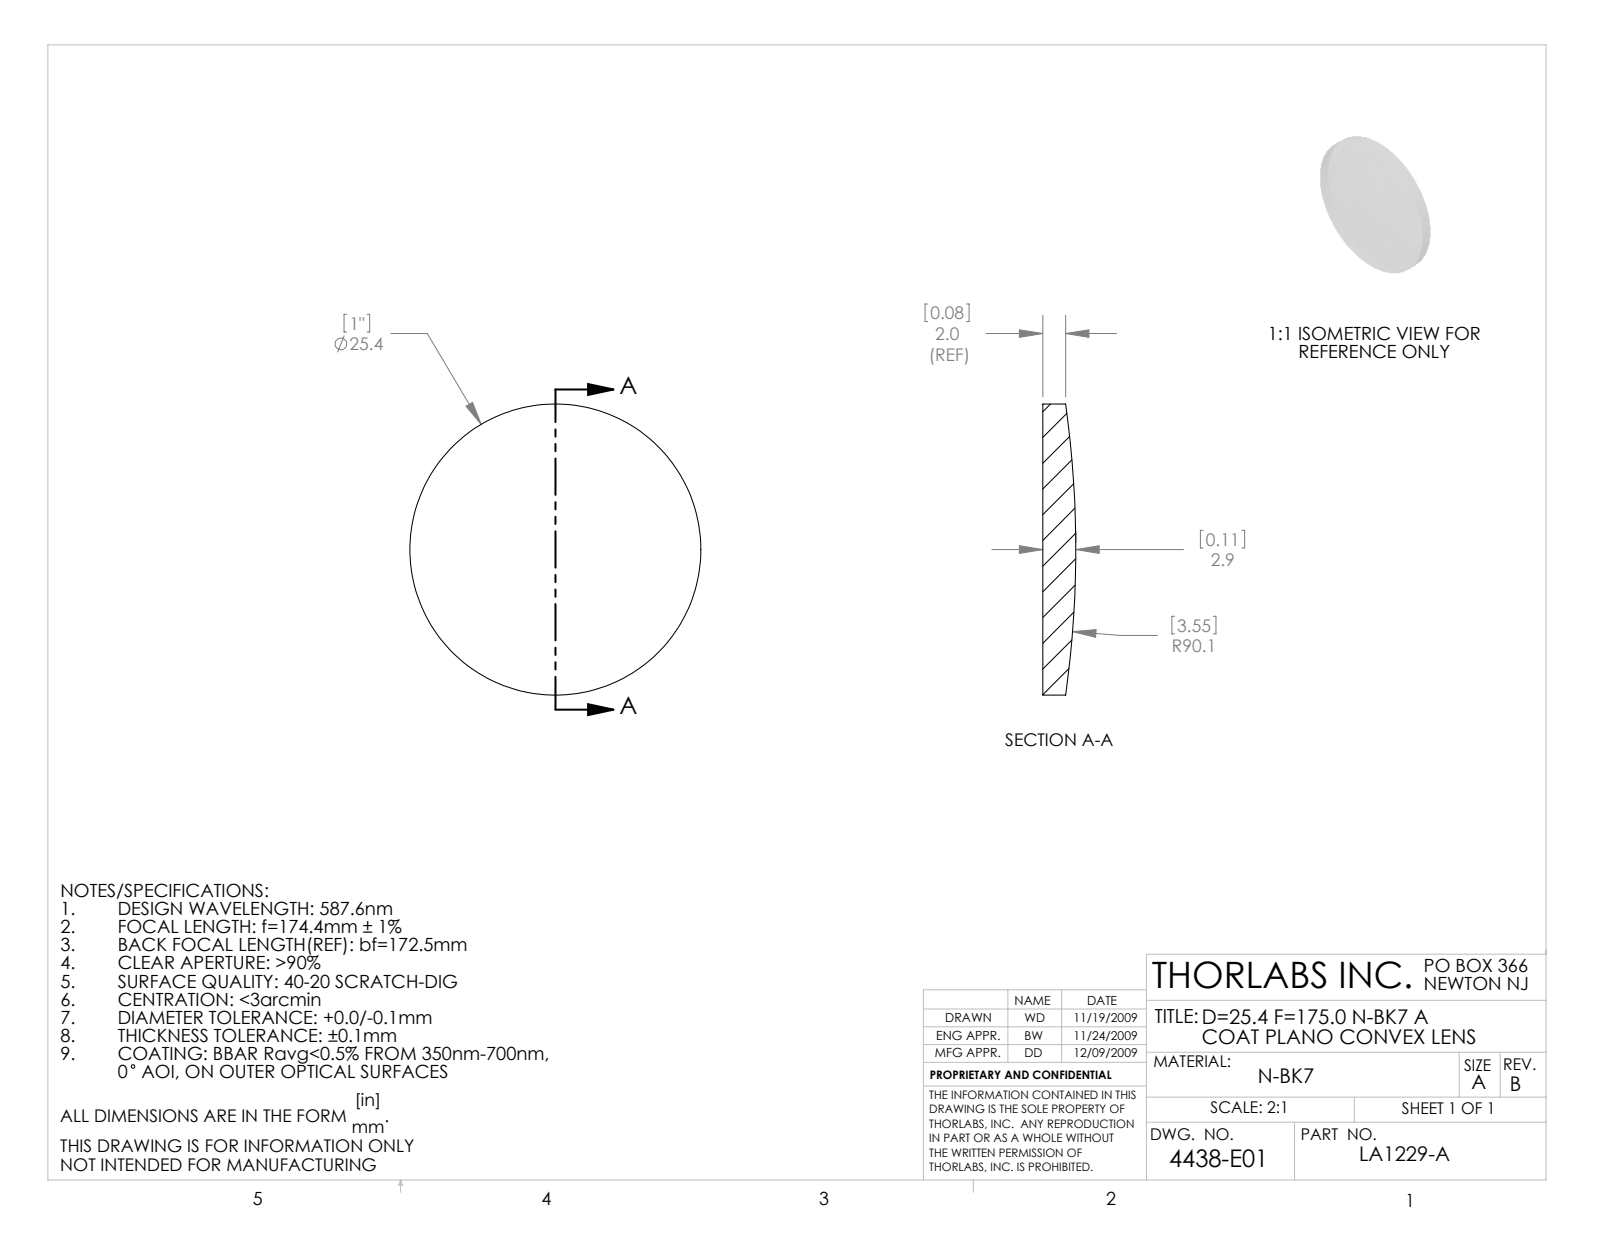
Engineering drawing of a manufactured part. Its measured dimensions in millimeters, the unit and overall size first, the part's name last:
Units: millimetres
Overall size (bounding box): 25.4 × 25.4 × 2.89
Round bosses / shafts (diameter × count): ⌀25.4 ×1
Volume: 1 237 mm³ · Surface area: 1 175 mm²
Bodies: 1 solid, 5 faces (1 planar, 2 cylindrical, 2 other)
Part name (STEP PRODUCT): 4438-E0W
STEP written by: SolidWorks 2009 (AUTOMOTIVE_DESIGN)
